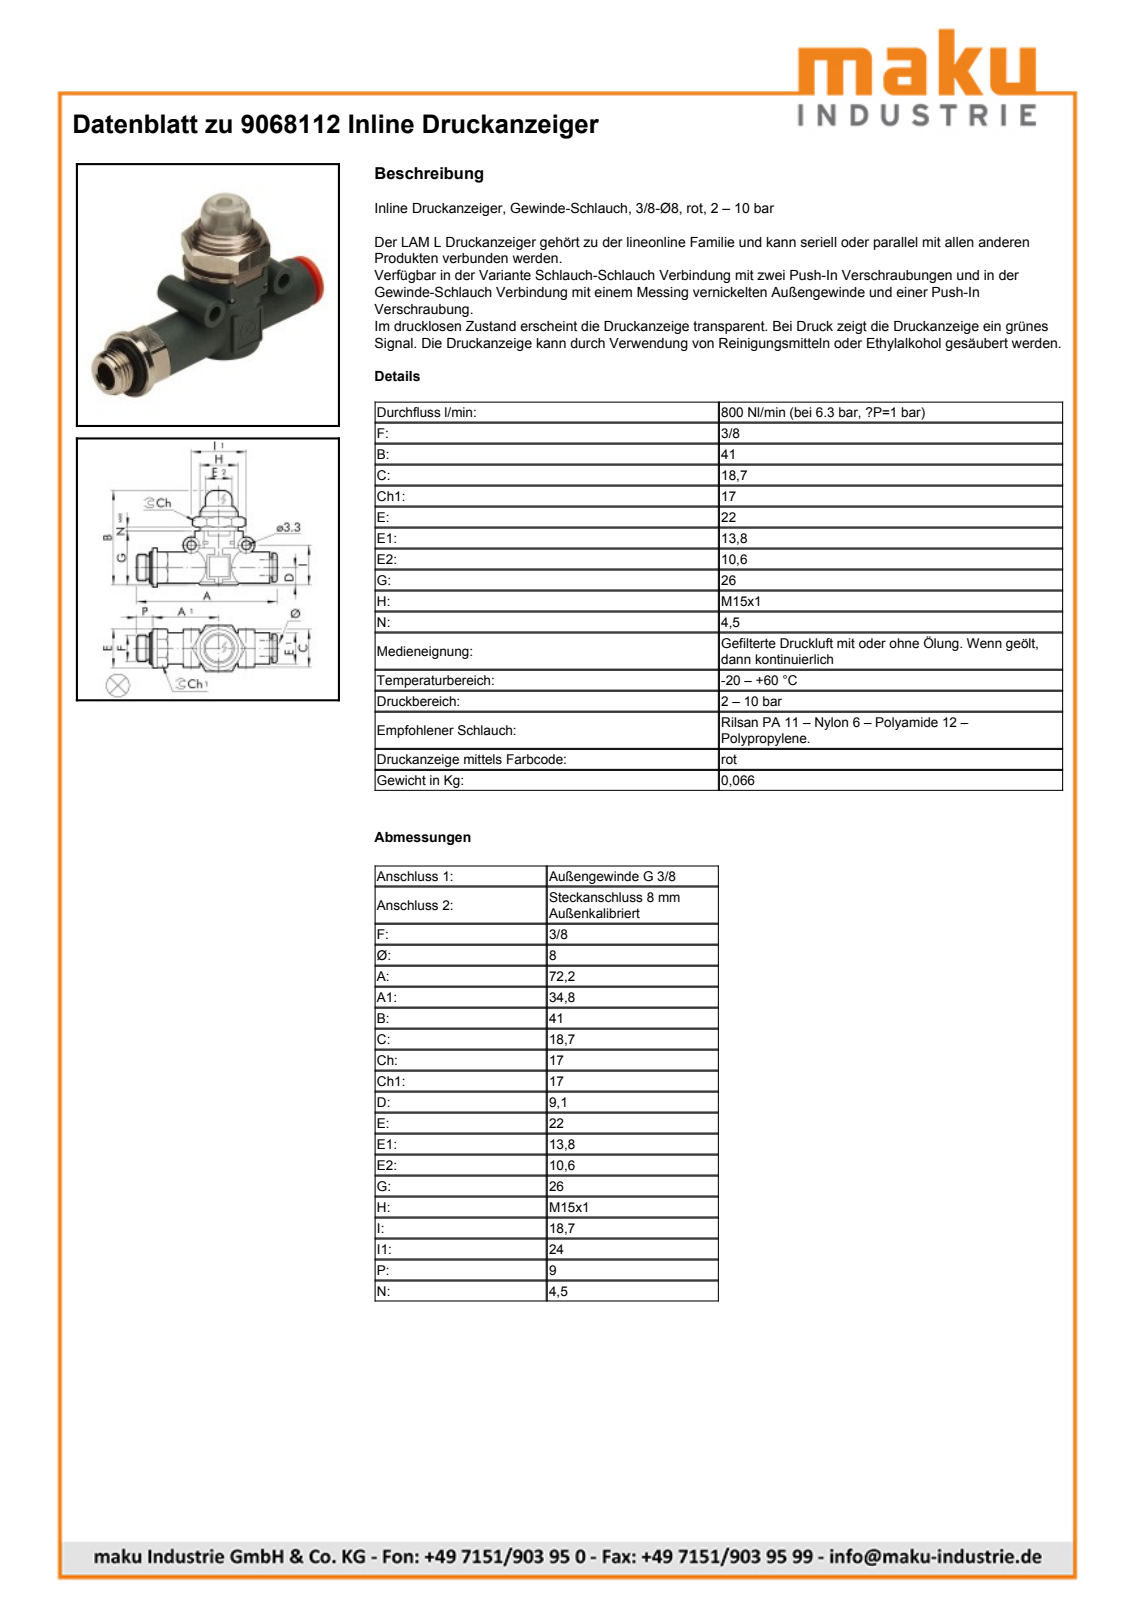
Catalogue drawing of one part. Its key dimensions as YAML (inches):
part_name: "9068112; LINE-ON-LINE D8 V2v/V3V_L body; LINE-ON-LINE D8 VNR-L bushing; LINE-ON-LINE D8-3/8 thread port (+1 more)"
step_written_by: "PARTsolutions (AUTOMOTIVE_DESIGN)"
units: inches
bodies: {solids: 4, faces: 183, planar: 94, cylindrical: 58, other: 31}
overall_size: [2.843, 1.689, 0.866]
volume: 0.842
surface_area: 17.43
round_holes:
  - {diameter: 0.13, count: 2}
  - {diameter: 0.236, count: 2}
  - {diameter: 0.217, count: 1}
  - {diameter: 0.319, count: 1}
  - {diameter: 0.394, count: 1}
  - {diameter: 0.433, count: 1}
  - {diameter: 0.459, count: 1}
  - {diameter: 0.492, count: 1}
  - {diameter: 0.591, count: 1}
round_bosses_or_shafts:
  - {diameter: 0.236, count: 2}
  - {diameter: 0.866, count: 1}
  - {diameter: 0.74, count: 1}
  - {diameter: 0.656, count: 1}
  - {diameter: 0.575, count: 1}
  - {diameter: 0.551, count: 1}
  - {diameter: 0.543, count: 1}
  - {diameter: 0.535, count: 1}
partial_cylinders:
  - {radius: 0.148, count: 1}
  - {radius: 0.378, count: 1}
  - {radius: 0.38, count: 1}
  - {radius: 0.402, count: 1}
  - {radius: 0.407, count: 1}
  - {radius: 0.451, count: 1}
face_to_face_distances: [0.949, 0.669, 0.075, 0.465, 0.161, 0.787, 0.157, 1.024, 0.862, 0.03]
hole_center_spacings: [0.605, 0.945]
